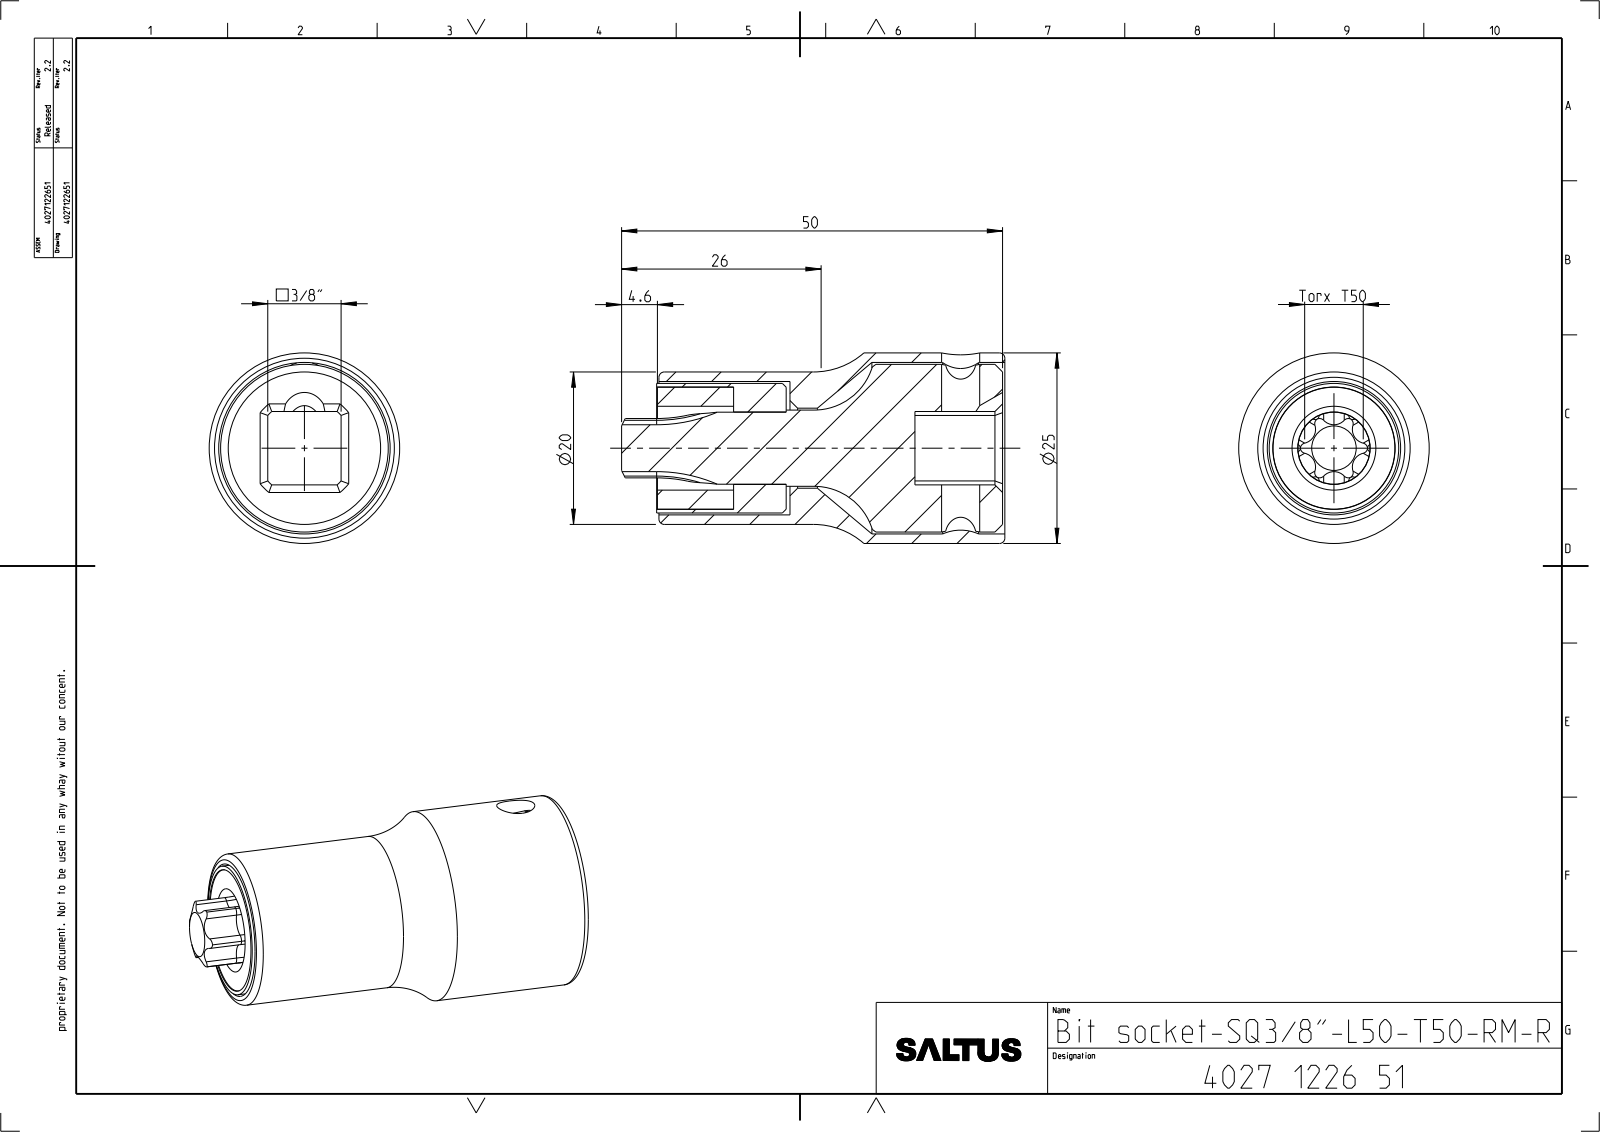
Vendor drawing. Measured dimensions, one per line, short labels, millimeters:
name: 4027905847; 4027901683; 4027907744; 4027904099_ASM (+2 more)
written by: CREO PARAMETRIC BY PTC INC, 2022414 (CONFIG_CONTROL_DESIGN)
unit: mm
bodies: 4 solids, 137 faces (21 planar, 65 cylindrical, 51 other)
size: 50.3 × 25 × 25
volume: 14 783 mm³; area: 12 564 mm²
holes: 1× ⌀5, 1× ⌀9.5, 1× ⌀10.5, 1× ⌀11, 1× ⌀16.1, 1× ⌀17.5, 1× ⌀22.5
bosses: 1× ⌀25, 1× ⌀22, 1× ⌀20, 1× ⌀17, 1× ⌀16, 1× ⌀10, 1× ⌀9.45
rounds: 12× R0.74, 6× R1.85, 1× R3, 1× R4.42, 1× R6.45
face distances: 16.9, 35.3, 9.62, 28.4, 6.9, 27.9, 0.5, 7.4, 45.3, 17.4
